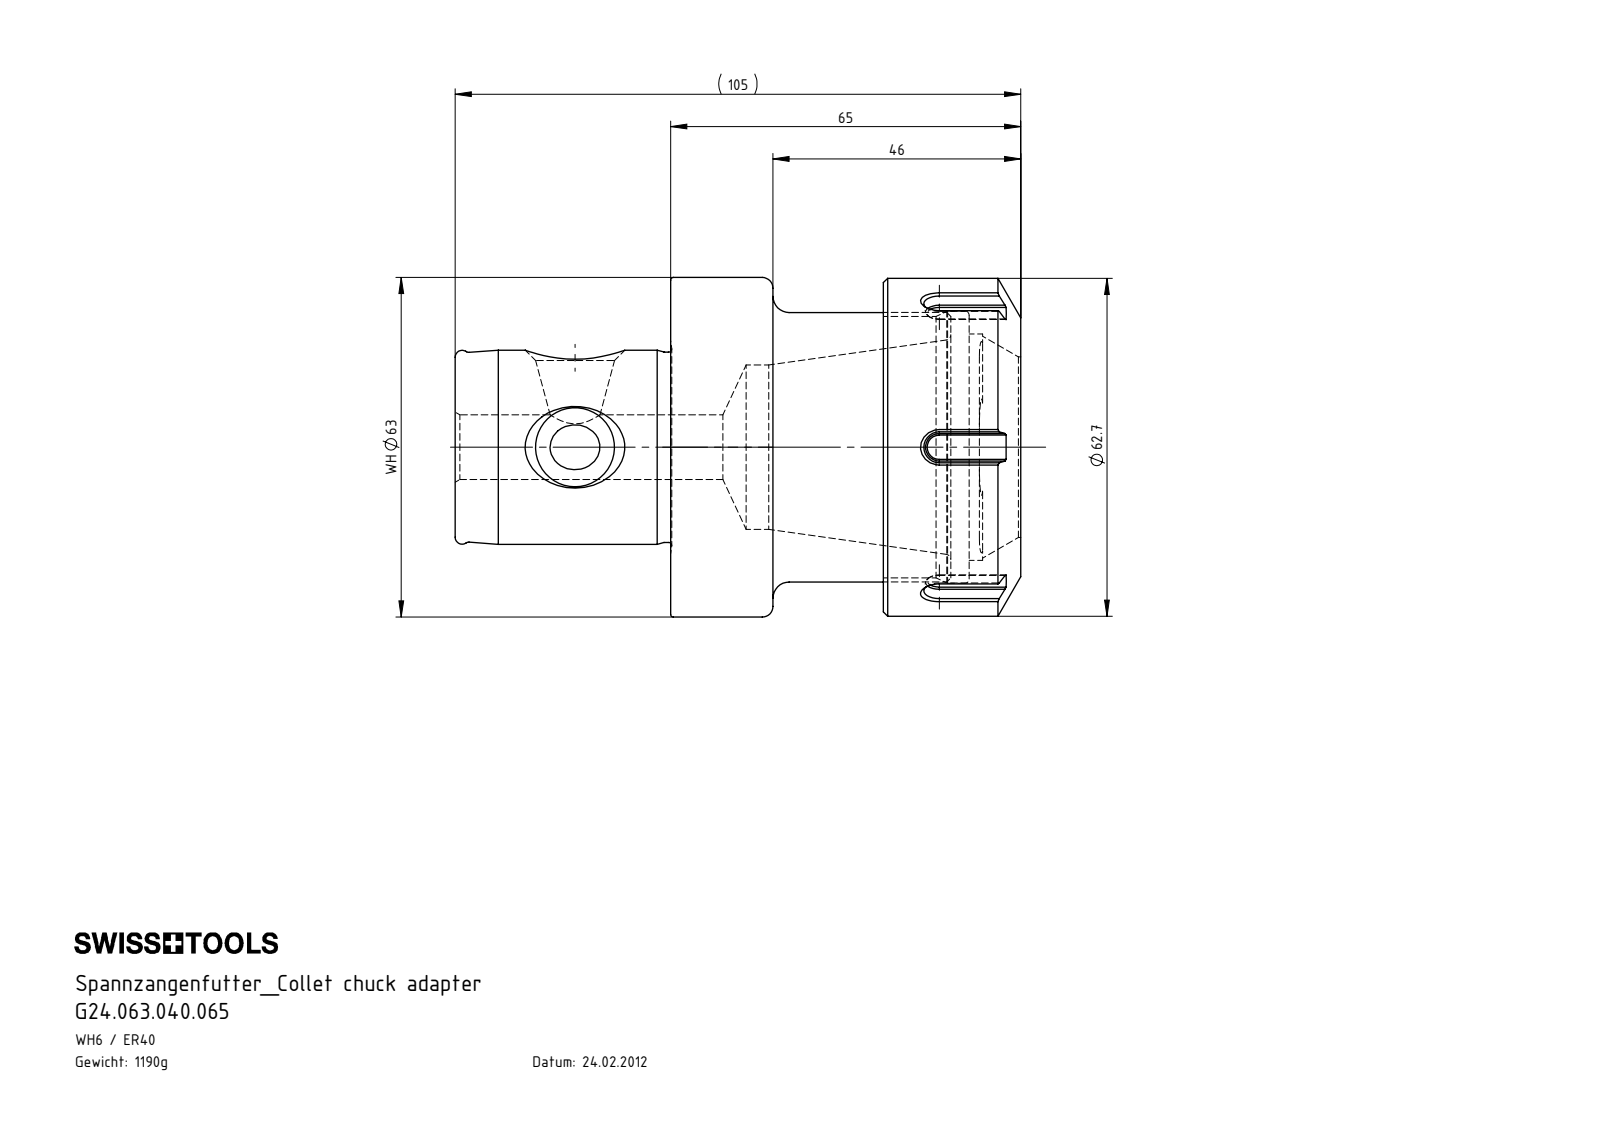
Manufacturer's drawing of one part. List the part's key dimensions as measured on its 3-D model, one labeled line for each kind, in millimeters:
Part name (STEP PRODUCT): WH6-E40.K01.065; WH6.E40.K01.065; E40-ER1.001.025
STEP written by: SolidWorks 2022 (AUTOMOTIVE_DESIGN)
Units: millimetres
Bodies: 2 solids, 150 faces (55 planar, 23 cylindrical, 72 other)
Overall size (bounding box): 105 × 63 × 63
Volume: 151 572 mm³ · Surface area: 37 421 mm²
Round holes (diameter × count): ⌀12 ×1, ⌀30.5 ×1, ⌀33.5 ×1, ⌀48.5 ×1, ⌀50.5 ×1
Round bosses / shafts (diameter × count): ⌀63 ×1, ⌀62.7 ×1, ⌀50 ×1, ⌀36 ×1, ⌀35.3 ×1
Partial cylindrical surfaces — rounded edges, fillets, slot ends (radius × count): R19.26 ×2
Main face-to-face distances: 39.5, 65, 25.5, 40, 79.5, 105, 95.4, 55.4, 15.9, 9.6
